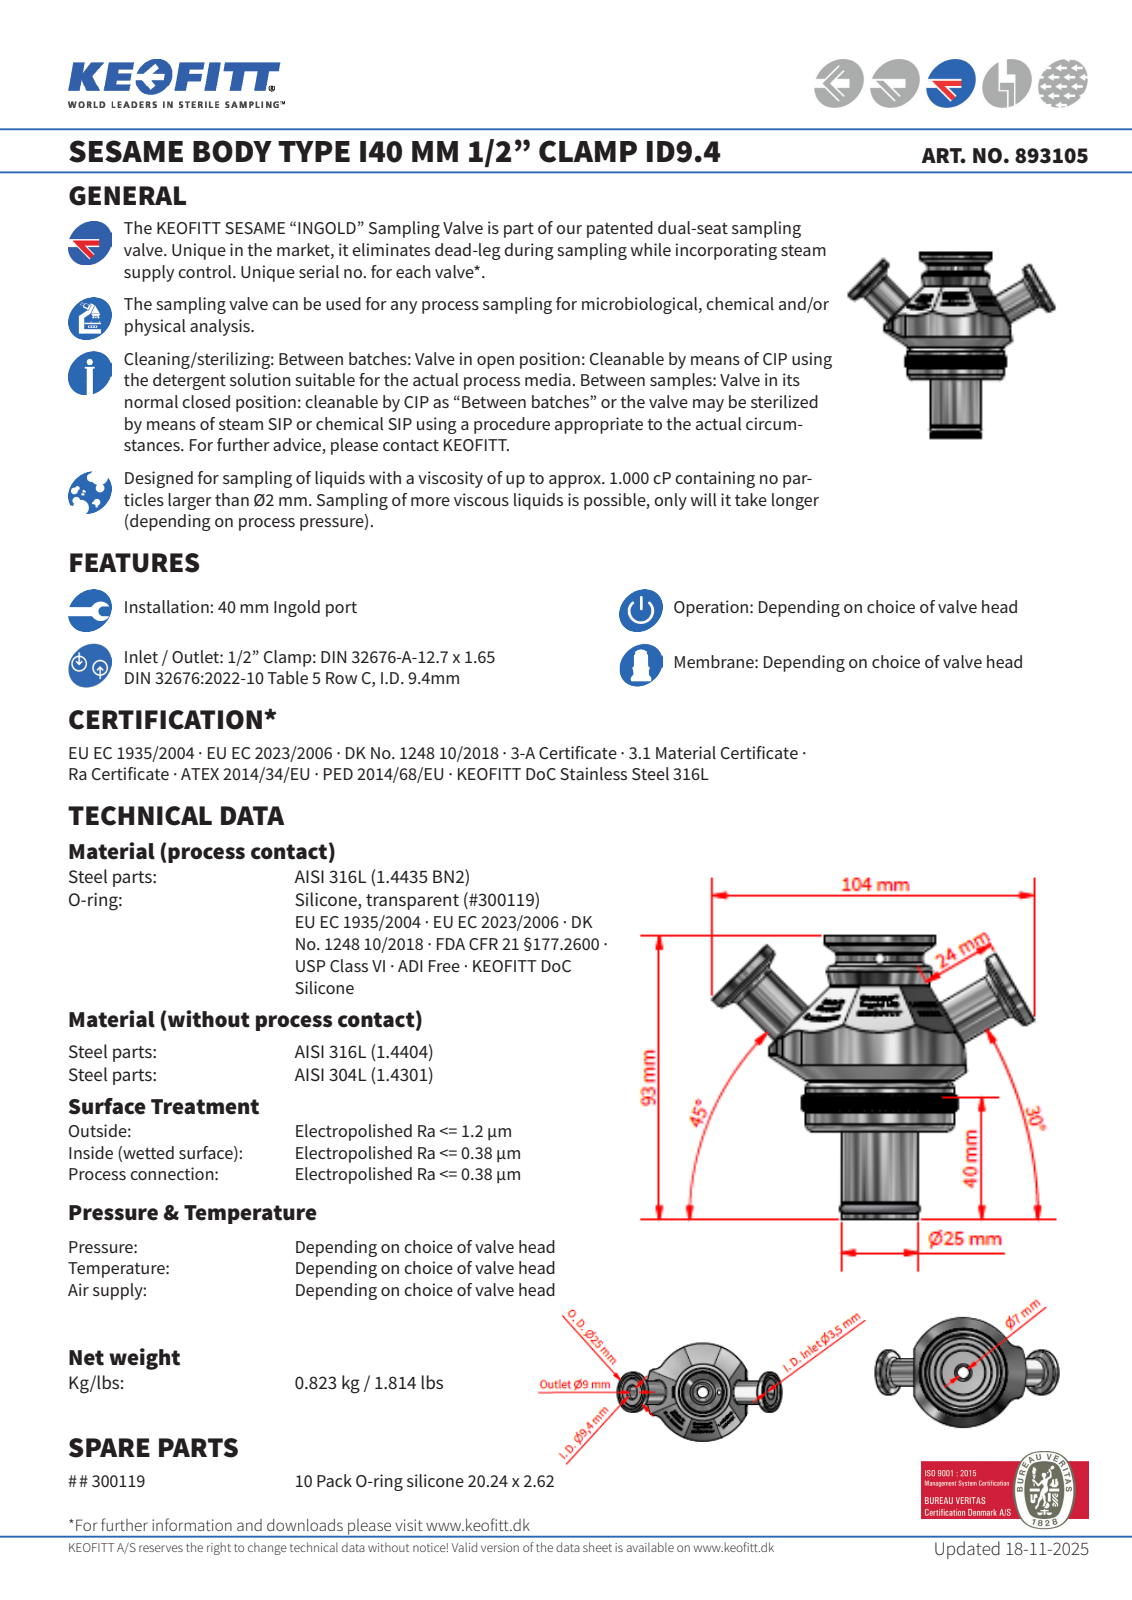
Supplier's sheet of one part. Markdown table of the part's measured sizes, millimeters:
| quantity | value |
| --- | --- |
| part name | 893105; 893105_Simplify_2 |
| STEP written by | Autodesk Inventor 2022 (AUTOMOTIVE_DESIGN) |
| units | millimeters |
| bodies | 5 solids, 100 faces (31 planar, 30 cylindrical, 39 other) |
| overall size | 104.39 × 92.5 × 62 |
| volume | 131 689 mm³ |
| surface area | 30 155 mm² |
| round holes (diameter × count) | 21.8 × 2, 30 × 1, 32 × 1, 36.4 × 1, 39 × 1, 43 × 1 |
| round bosses / shafts (diameter × count) | 25 × 3, 15 × 2, 50 × 1, 48 × 1, 36 × 1, 28.7 × 1, 28.5 × 1, 28 × 1 |
| partial cylindrical surfaces (radius × count) | 7 × 2, 31 × 1, 36 × 1 |
| main face-to-face distances | 3, 49.5, 33, 2.5, 30.5, 46.5, 44, 13.5, 5.5, 36 |
